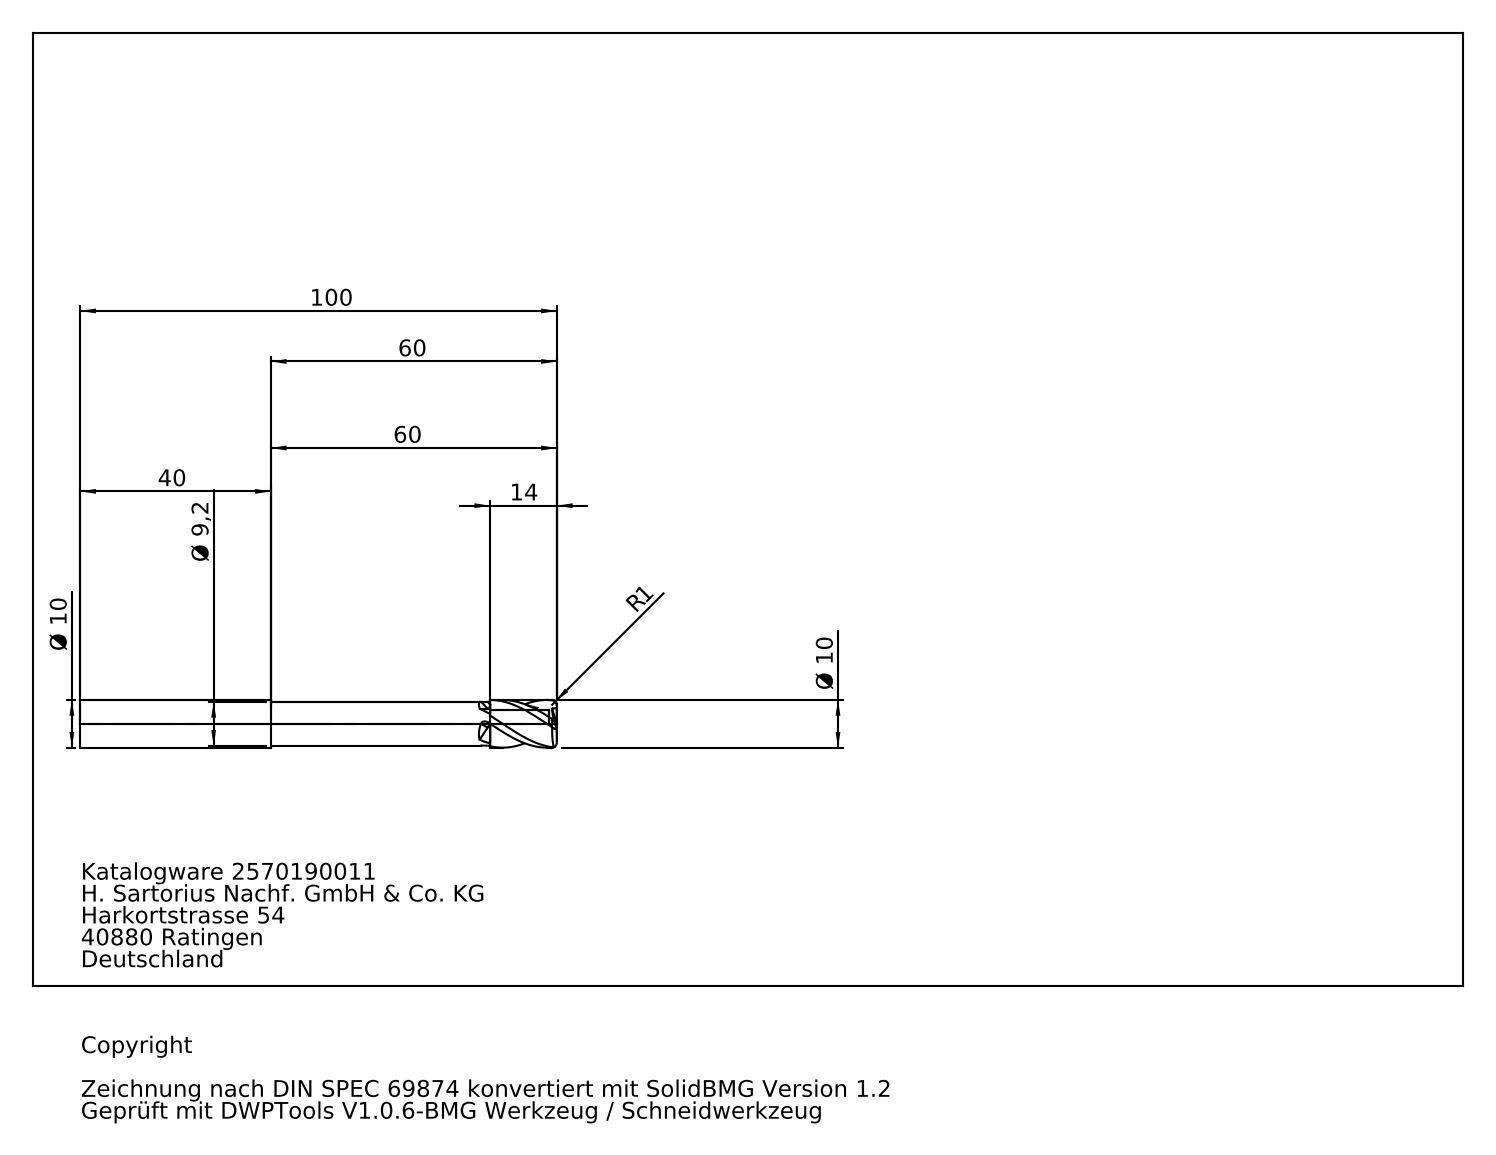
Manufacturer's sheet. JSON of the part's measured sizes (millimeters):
{"part_name": "2570190011", "step_written_by": "SolidWorks 2010 (AUTOMOTIVE_DESIGN)", "units": "millimeters", "bodies": {"solids": 2, "faces": 60, "planar": 15, "cylindrical": 18, "other": 27}, "overall_size": [100, 10, 10], "volume_mm3": 6888, "surface_area_mm2": 3772, "round_holes": [[6, 1]], "round_bosses_or_shafts": [[10, 1], [9.2, 1]], "face_to_face_distances": [98.39, 86, 12.39, 40, 46, 58.39, 99.97, 59.97, 13.97, 1.58]}
